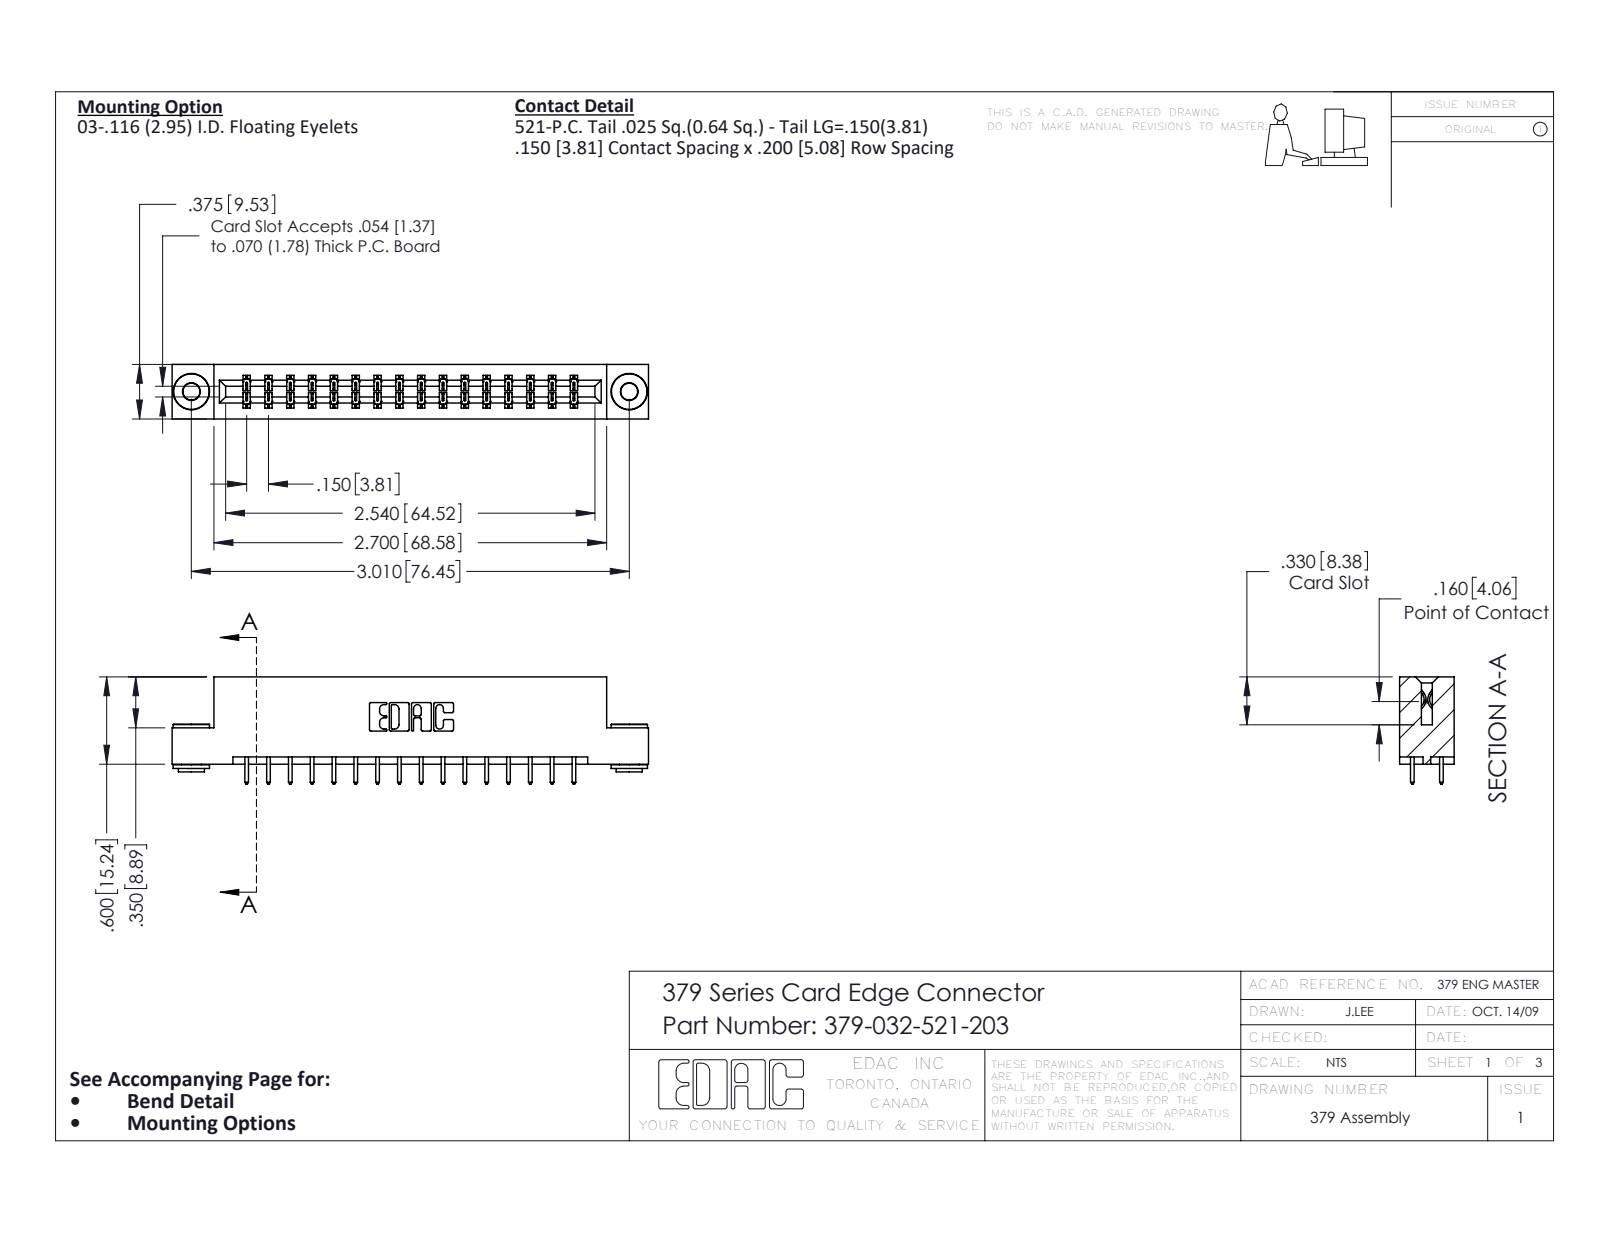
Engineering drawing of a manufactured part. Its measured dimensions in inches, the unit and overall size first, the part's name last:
Units: inches
Overall size (bounding box): 3.275 × 0.737 × 0.375
Round holes (diameter × count): ⌀0.116 ×2, ⌀0.156 ×2
Round bosses / shafts (diameter × count): ⌀0.25 ×2, ⌀0.18 ×2, ⌀0.136 ×2
Partial cylindrical surfaces — rounded edges, fillets, slot ends (radius × count): R0.006 ×63, R0.01 ×32, R0.01 ×22, R0.007 ×6, R0.031 ×6, R0.026 ×3, R0.014 ×2, R0.022 ×2
Main face-to-face distances: 0.3, 0.075, 0.2, 0.375, 0.1, 0.15, 0.05, 0.6, 0.225, 0.55
Hole centre spacings: 3.01
Volume: 0.521 in³ · Surface area: 14.7 in²
Bodies: 35 solids, 1816 faces (1232 planar, 576 cylindrical, 8 other)
Part name (STEP PRODUCT): 345-292-001_345-293-121; 379-032-521-203; 345-250-002_345-250-002-102; 379 Part_Flush - .156 Dia - TH
STEP written by: SolidWorks 2020 (CONFIG_CONTROL_DESIGN)
